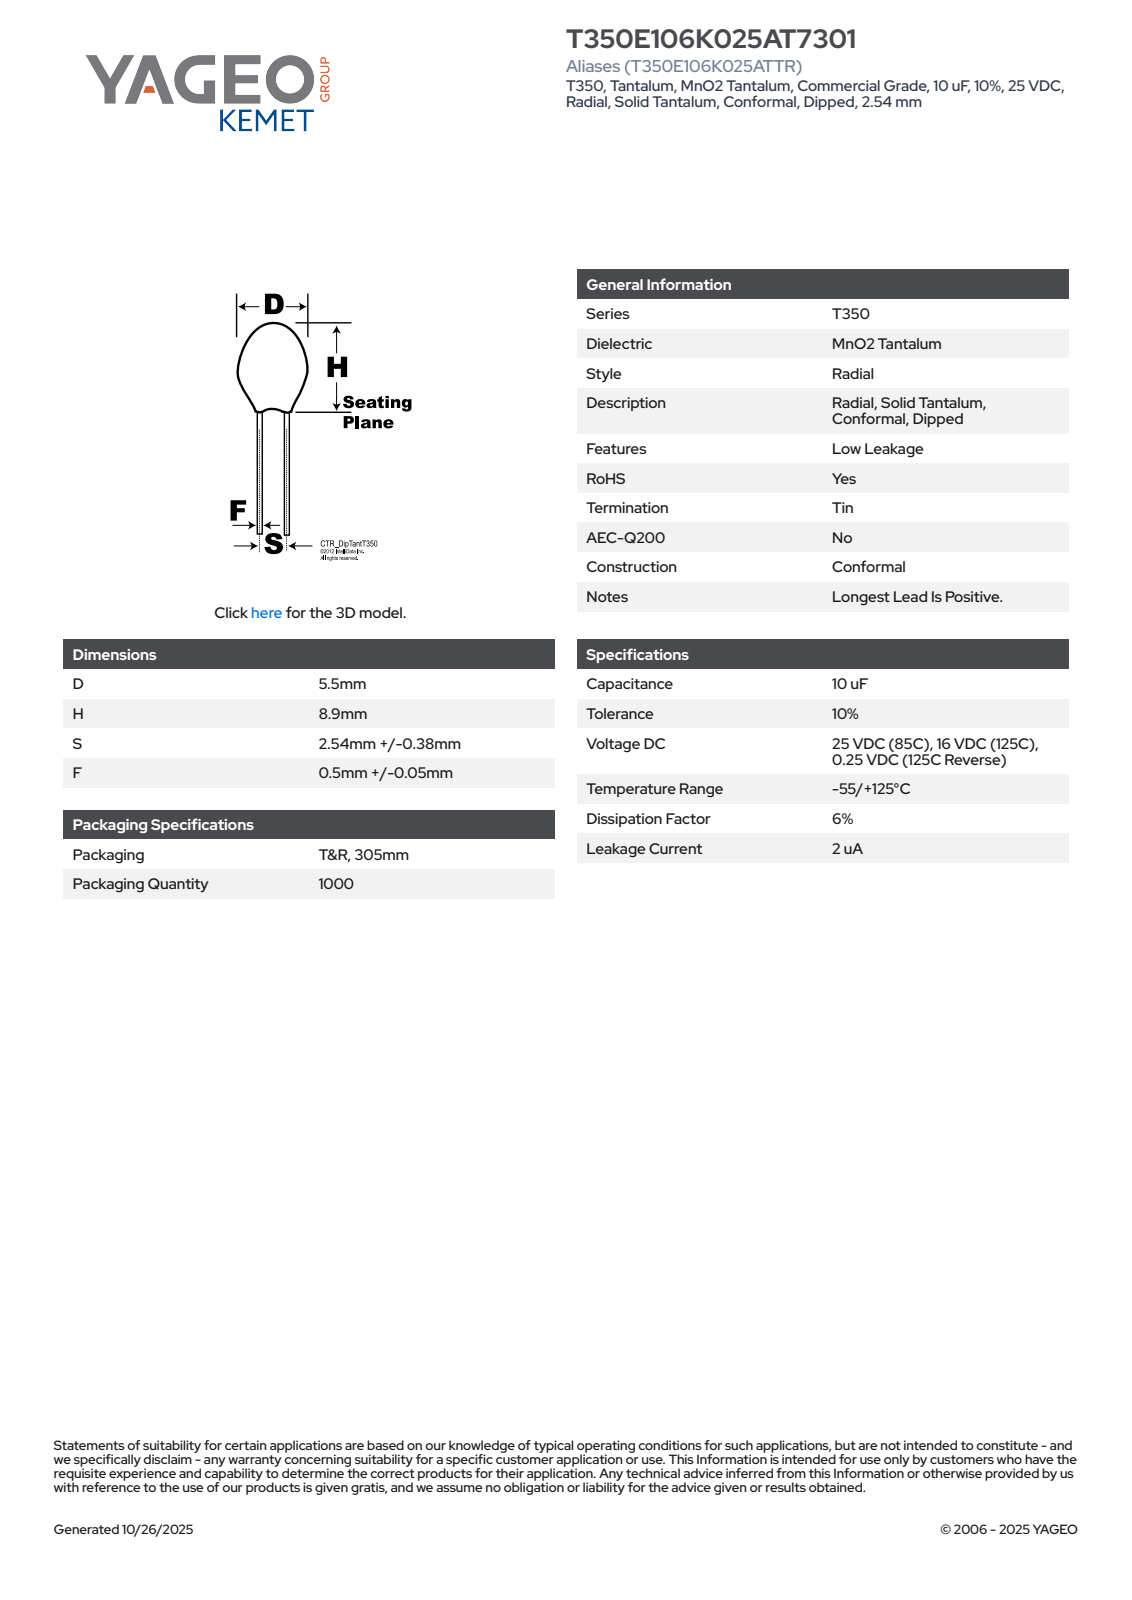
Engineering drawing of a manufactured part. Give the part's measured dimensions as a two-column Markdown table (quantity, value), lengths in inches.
| quantity | value |
| --- | --- |
| part name | CTR_T350_D5.5H8.9S2.54LL13.96F0.55 |
| STEP written by | SolidWorks 2014 (AUTOMOTIVE_DESIGN) |
| units | inches |
| bodies | 1 solid, 73 faces (26 planar, 10 cylindrical, 37 other) |
| overall size | 0.9 × 0.217 × 0.217 |
| volume | 0.011 in³ |
| surface area | 0.33 in² |
| round bosses / shafts (diameter × count) | 0.022 × 2, 0.217 × 1 |
| partial cylindrical surfaces (radius × count) | 0.108 × 1 |
| main face-to-face distances | 0.35, 0.55, 0.9, 0.742, 0.192, 0.158, 0.71, 0.16, 0.032, 0.19 |
